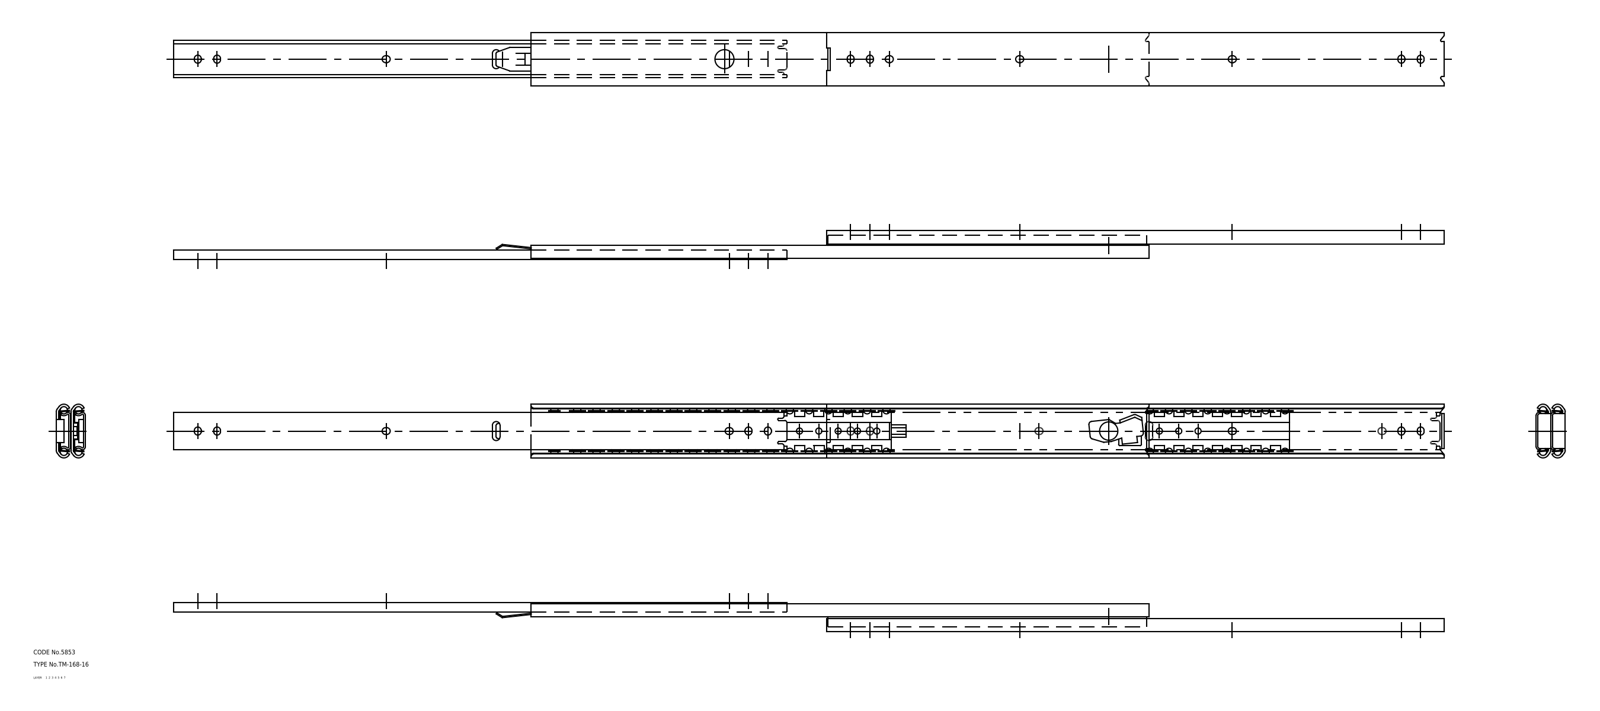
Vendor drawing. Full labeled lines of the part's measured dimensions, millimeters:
Part name (STEP PRODUCT): ball; retainer_2; retainer_1; member_C (+3 more)
STEP written by: CADfix (AUTOMOTIVE_DESIGN)
Units: millimetres
Bodies: 89 solids, 1431 faces (0 planar, 0 cylindrical, 1431 other)
Overall size (bounding box): 835 × 35.3 × 19.1
Volume: 89 803 mm³ · Surface area: 149 230 mm²
